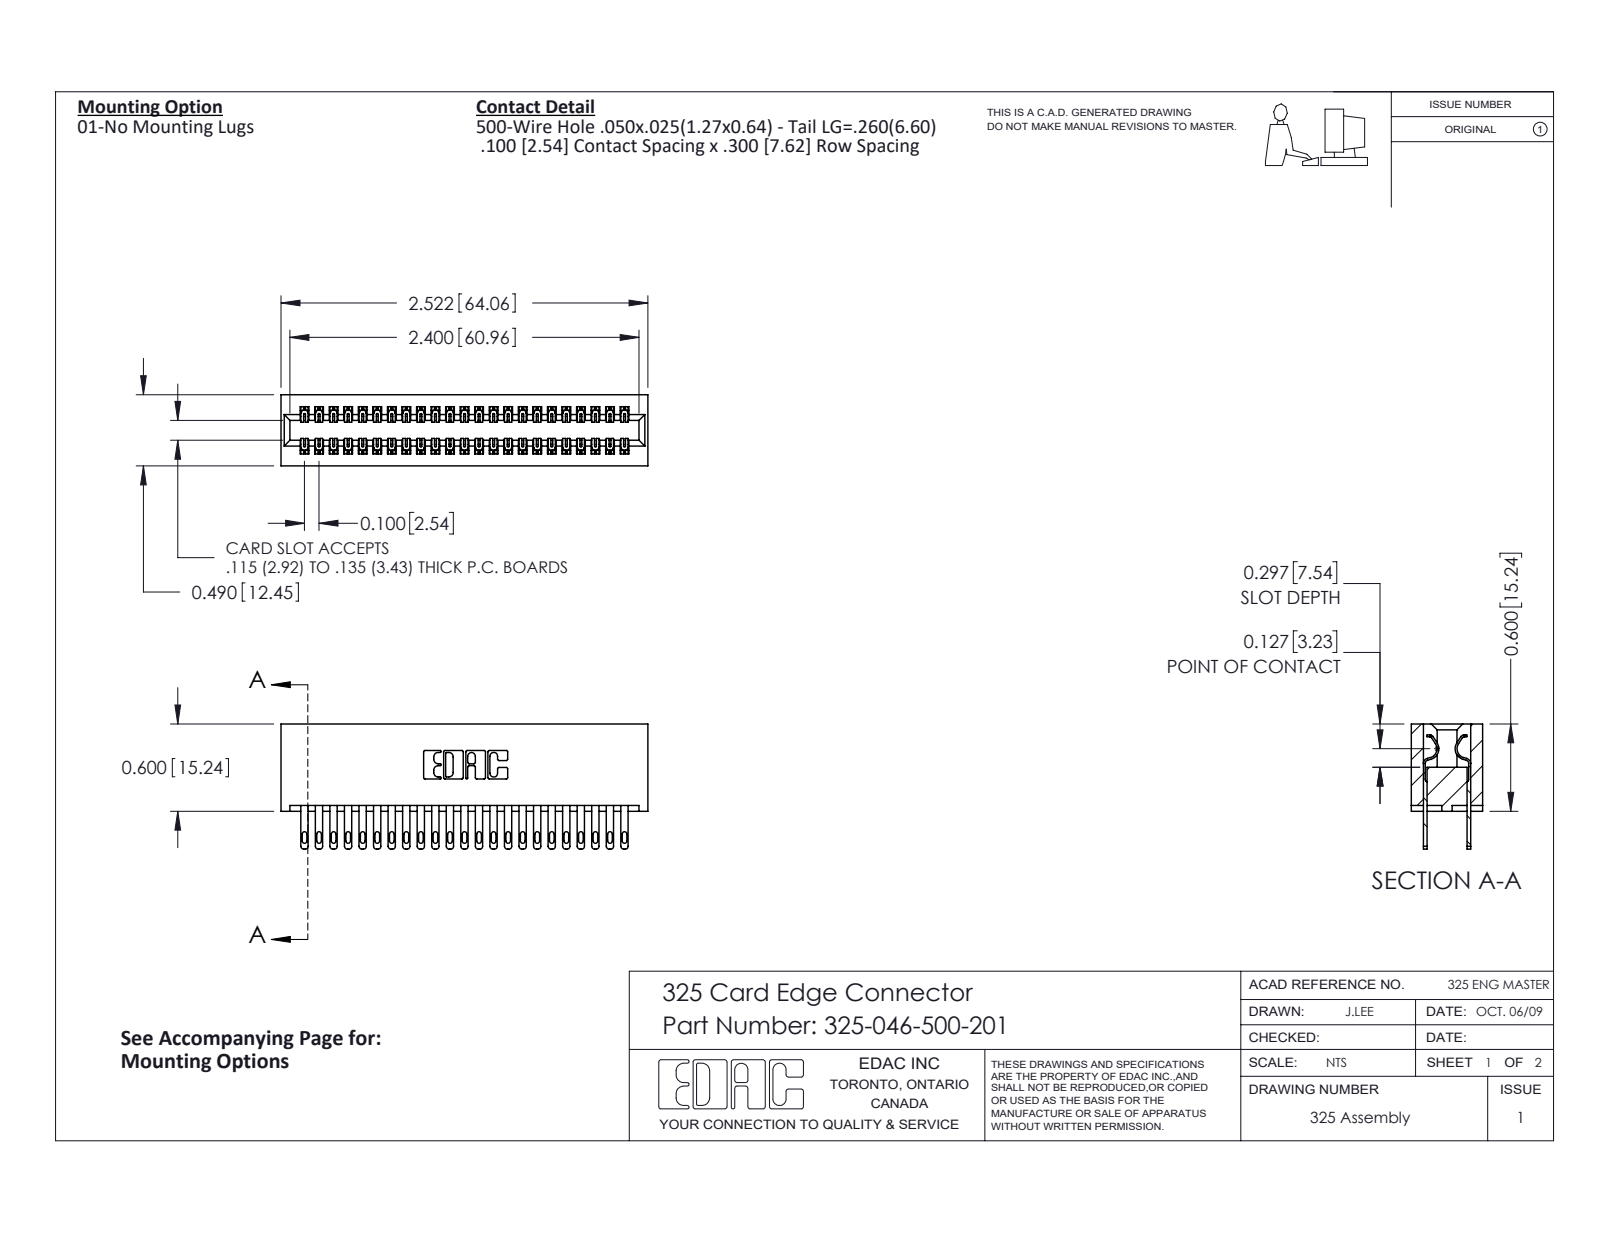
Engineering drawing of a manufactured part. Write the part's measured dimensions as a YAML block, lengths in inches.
part_name: "325-292-001_325-293-100; 325 Part_Lugless; 325-046-500-201"
step_written_by: "SolidWorks 2016 (CONFIG_CONTROL_DESIGN)"
units: inches
bodies: {solids: 47, faces: 2314, planar: 1446, cylindrical: 868, other: 0}
overall_size: [2.522, 0.86, 0.49]
volume: 0.54
surface_area: 17.67
partial_cylinders:
  - {radius: 0.006, count: 69}
  - {radius: 0.016, count: 46}
  - {radius: 0.02, count: 46}
  - {radius: 0.01, count: 22}
  - {radius: 0.007, count: 6}
  - {radius: 0.031, count: 6}
  - {radius: 0.026, count: 3}
  - {radius: 0.014, count: 2}
face_to_face_distances: [0.083, 0.407, 0.3, 0.107, 0.383, 0.025, 0.325, 0.49, 0.275, 0.56]
